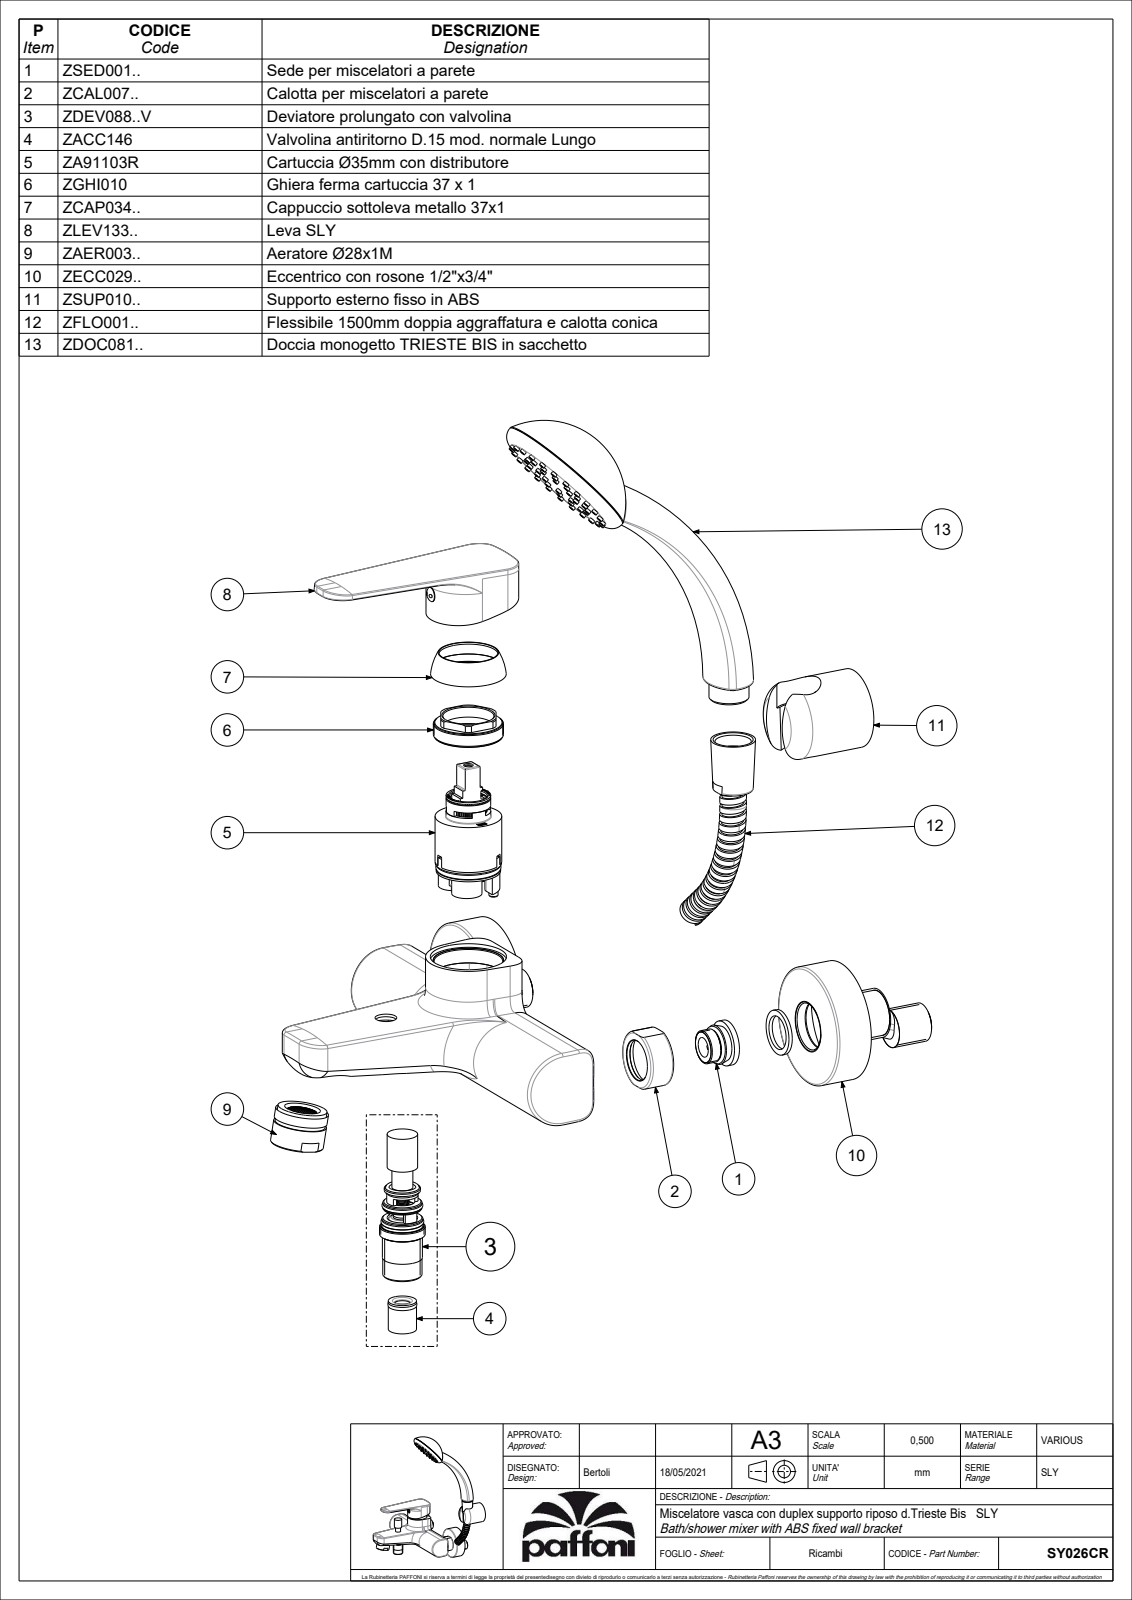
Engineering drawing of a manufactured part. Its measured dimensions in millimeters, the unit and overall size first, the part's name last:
Units: millimetres
Overall size (bounding box): 359.2 × 321.99 × 165
Round holes (diameter × count): ⌀5 ×4, ⌀8 ×4, ⌀12 ×4, ⌀9 ×3, ⌀19 ×3, ⌀24.5 ×3, ⌀25 ×3, ⌀3.3 ×2, ⌀4 ×2, ⌀10.5 ×2, ⌀16.5 ×2, ⌀18 ×2
Round bosses / shafts (diameter × count): ⌀24 ×3, ⌀63.5 ×2, ⌀27 ×2, ⌀12 ×2, ⌀10 ×2, ⌀75.5 ×1, ⌀72.5 ×1, ⌀65.8 ×1
Partial cylindrical surfaces — rounded edges, fillets, slot ends (radius × count): R0.5 ×56, R0.75 ×16, R0.15 ×11, R0.3 ×9, R1.5 ×6, R1 ×4, R7 ×4, R4.5 ×3
Main face-to-face distances: 3.5, 0.6, 15, 18.5, 3, 15.6, 26.5, 36.5, 19.1, 0.5
Hole centre spacings: 10.5, 24.85, 0.71, 8.51, 8.6, 9, 13.04, 13.21
Volume: 438 679 mm³ · Surface area: 258 553 mm²
Bodies: 6 solids, 3839 faces (2383 planar, 542 cylindrical, 914 other)
Part name (STEP PRODUCT): SY026CR
STEP written by: CREO PARAMETRIC BY PTC INC, 2020044 (CONFIG_CONTROL_DESIGN)
